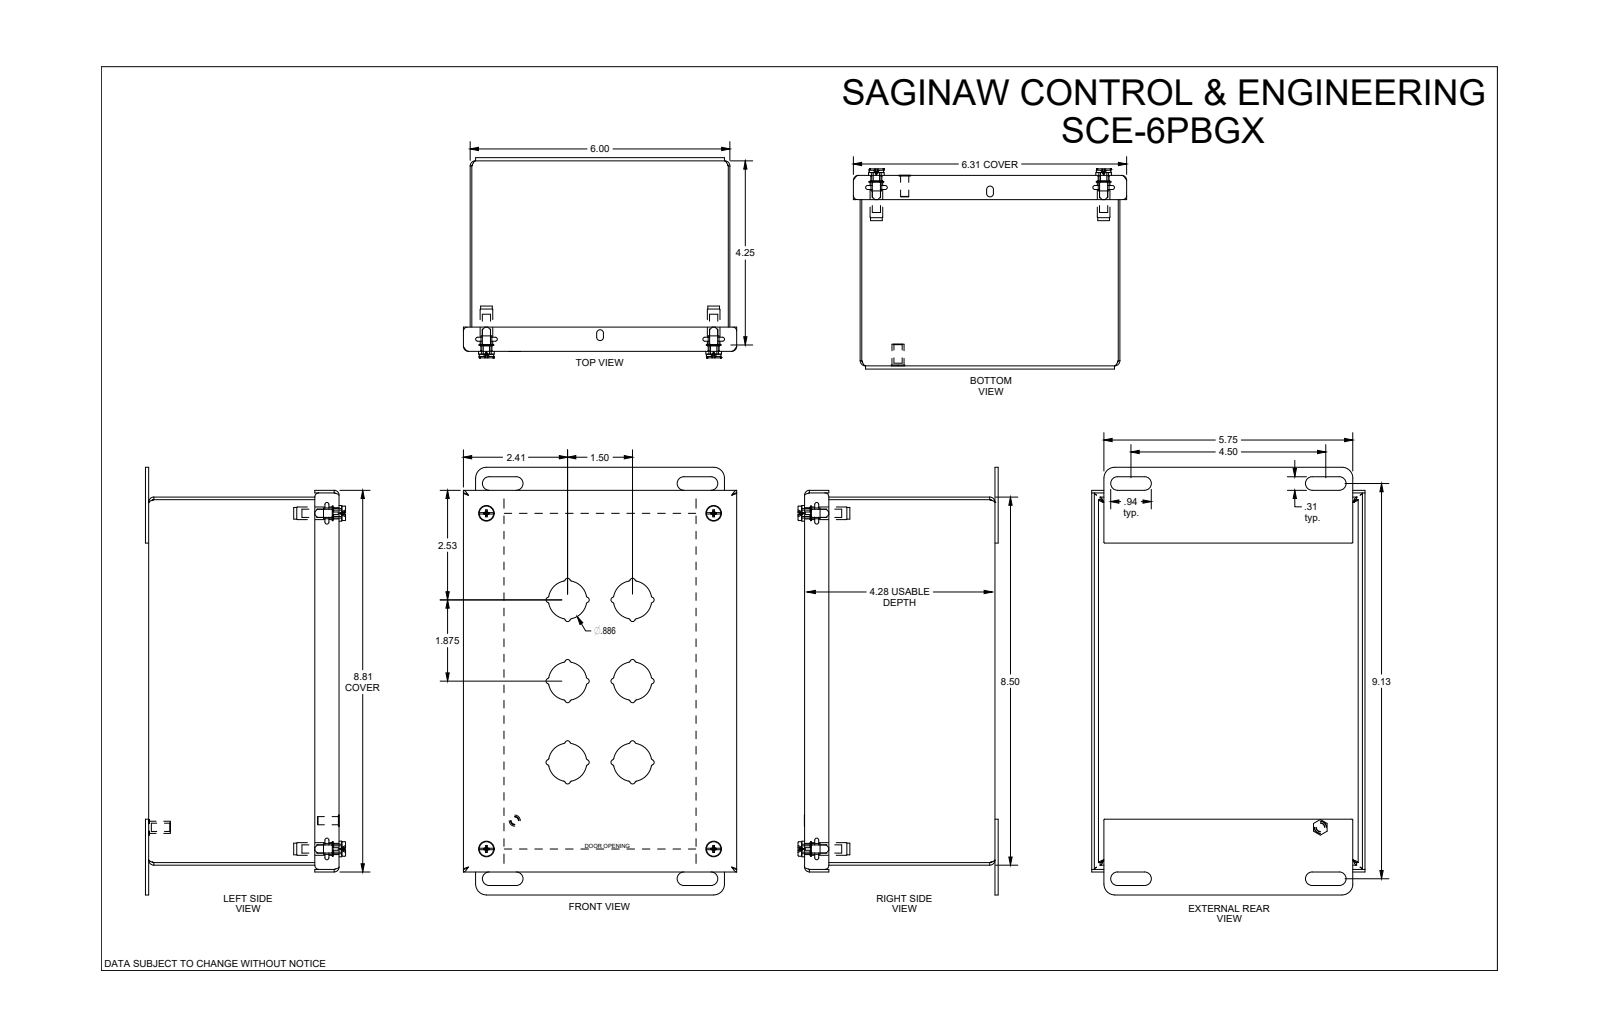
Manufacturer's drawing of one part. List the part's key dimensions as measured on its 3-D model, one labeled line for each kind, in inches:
Part name (STEP PRODUCT): SCE-6PBGX
STEP written by: SolidWorks 2021 (AUTOMOTIVE_DESIGN)
Units: inches
Bodies: 3 solids, 514 faces (154 planar, 276 cylindrical, 84 other)
Overall size (bounding box): 9.875 × 6.313 × 4.536
Volume: 16.96 in³ · Surface area: 538.5 in²
Round holes (diameter × count): ⌀0.19 ×5, ⌀0.22 ×4, ⌀0.25 ×4, ⌀0.266 ×4, ⌀0.317 ×4
Round bosses / shafts (diameter × count): ⌀0.362 ×4, ⌀0.34 ×4, ⌀0.292 ×4, ⌀0.27 ×4, ⌀0.26 ×4, ⌀0.28 ×1, ⌀0.256 ×1, ⌀0.188 ×1
Partial cylindrical surfaces — rounded edges, fillets, slot ends (radius × count): R0.04 ×48, R0.062 ×24, R0.06 ×20, R0.015 ×8, R0.115 ×8, R0.156 ×8, R0.245 ×8, R0.443 ×6
Main face-to-face distances: 0.06, 4.338, 5.94, 4.278, 8.44, 4.398, 6, 5.88, 0.156, 8.5
Hole centre spacings: 7.75, 9.361, 5.25, 5.25, 5.25, 7.267, 7.745, 8.667
